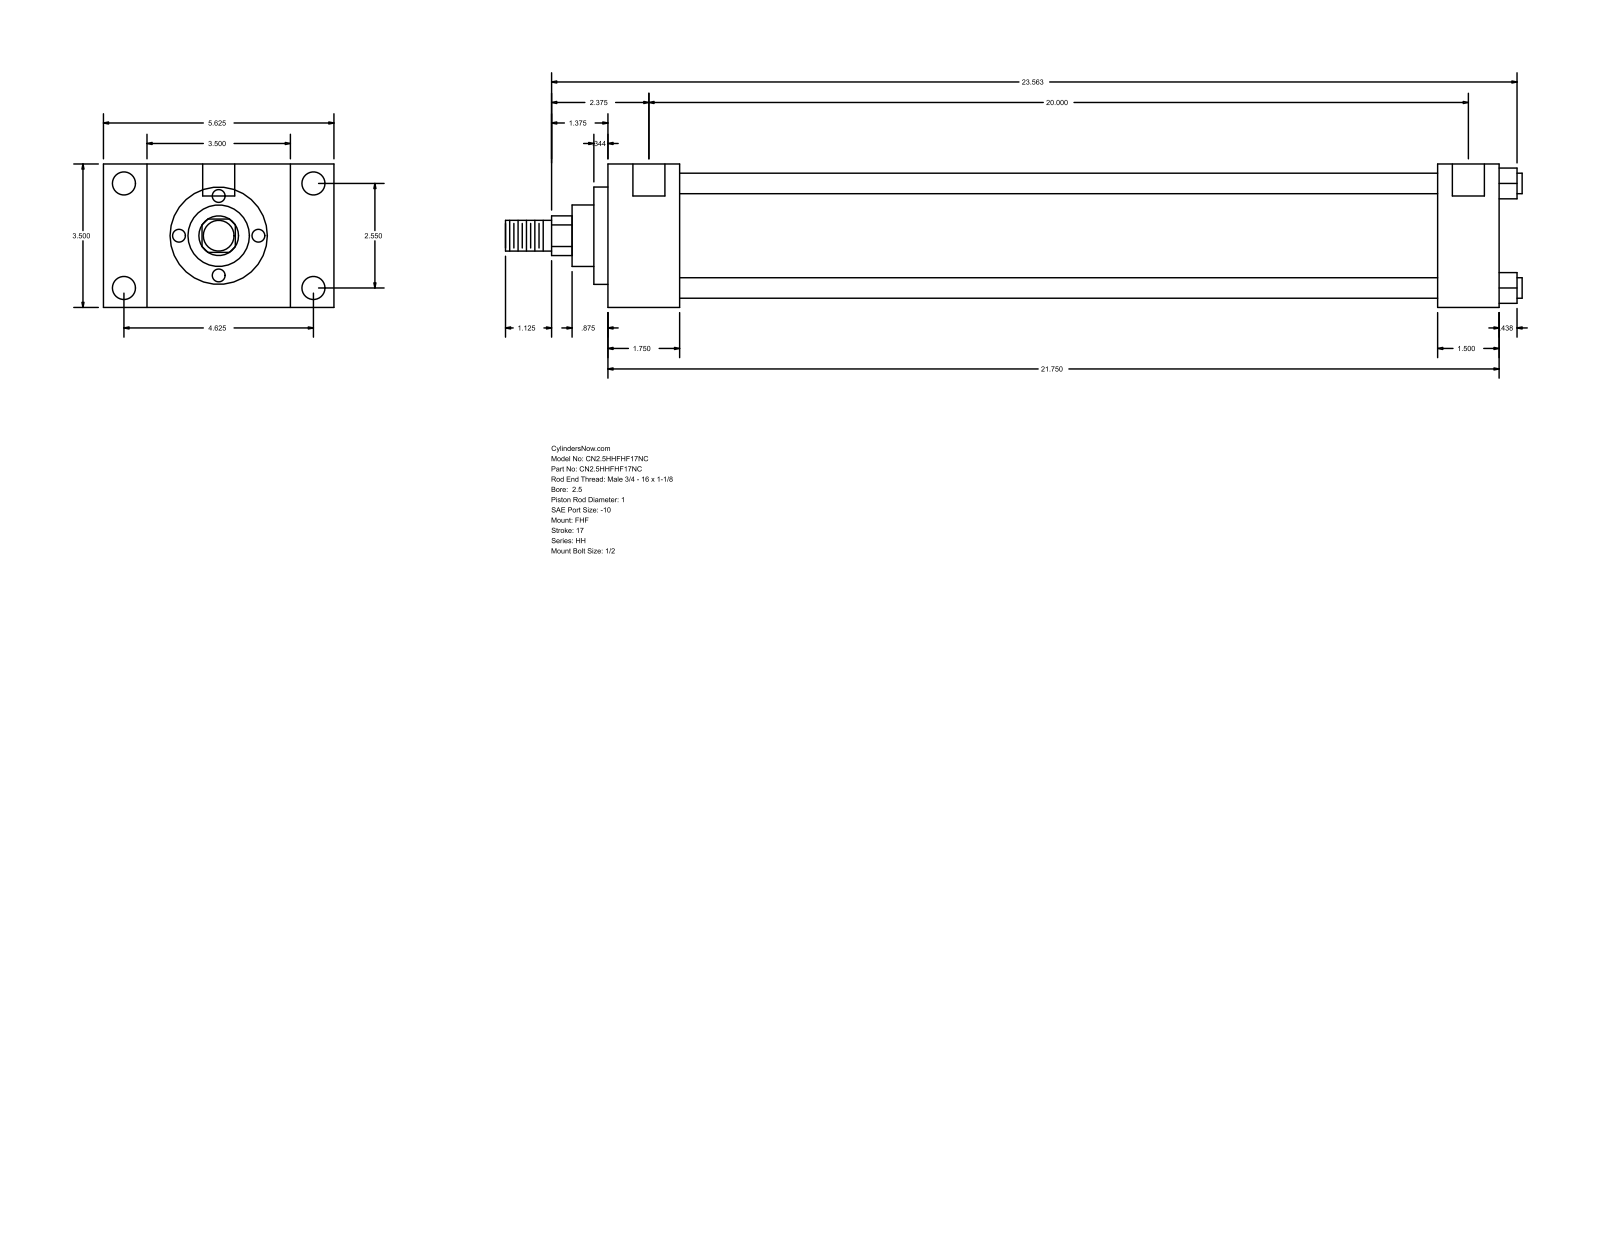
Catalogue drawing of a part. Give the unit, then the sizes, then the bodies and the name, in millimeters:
Units: millimetres
Overall size (bounding box): 630.24 × 142.88 × 88.9
Round holes (diameter × count): ⌀5.56 ×4, ⌀14.3 ×4, ⌀19.84 ×2
Round bosses / shafts (diameter × count): ⌀12.7 ×4, ⌀73.03 ×1, ⌀60.33 ×1, ⌀38.1 ×1, ⌀25.4 ×1, ⌀19.05 ×1
Partial cylindrical surfaces — rounded edges, fillets, slot ends (radius × count): R12.29 ×1
Main face-to-face distances: 88.9, 44.46, 26.99, 115.89, 552.46, 508, 142.88, 514.35, 469.89, 38.11
Hole centre spacings: 64.76, 117.48, 134.15, 511.17, 1.58, 1.59, 508, 509.58
Bodies: 0 solids, 90 faces (61 planar, 29 cylindrical, 0 other)
Part name (STEP PRODUCT): HH_FHF__0250_1
STEP written by: GSSL Pune (CONFIG_CONTROL_DESIGN)
